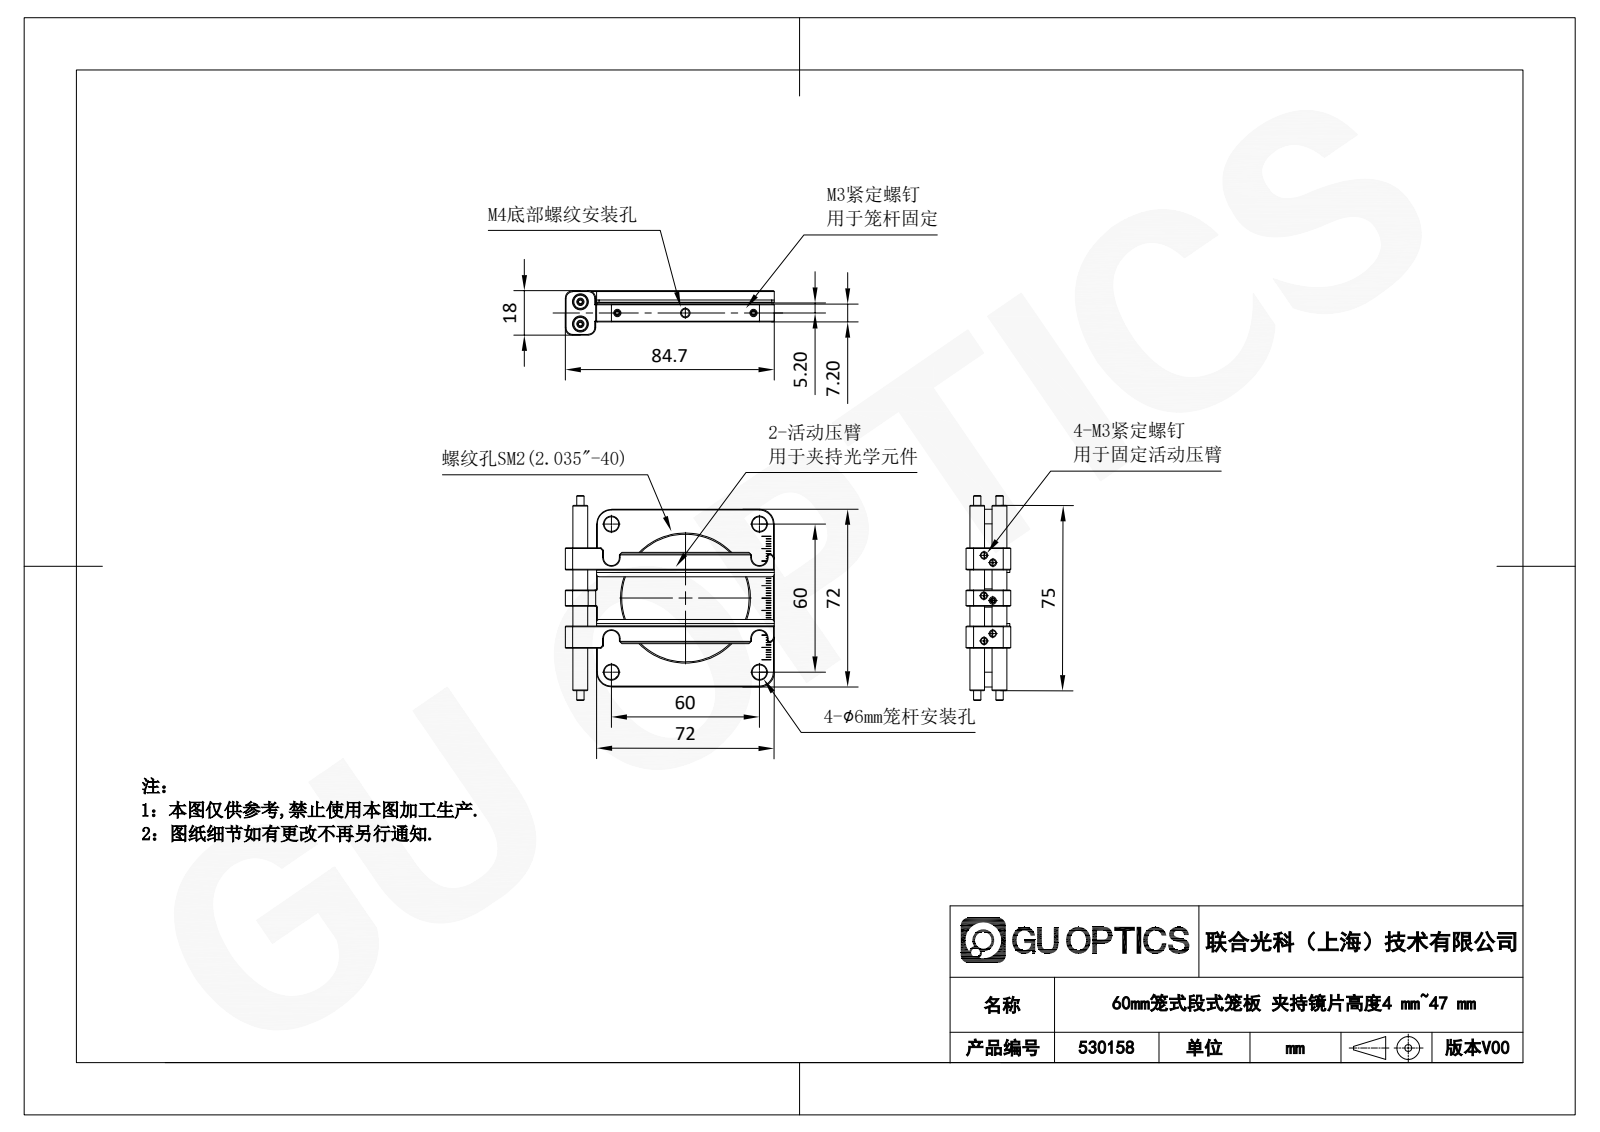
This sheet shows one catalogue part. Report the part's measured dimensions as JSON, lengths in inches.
{"part_name": "530158", "step_written_by": "SolidWorks 2020 (CONFIG_CONTROL_DESIGN)", "units": "inches", "bodies": {"solids": 16, "faces": 970, "planar": 745, "cylindrical": 65, "other": 160}, "overall_size": [3.335, 3.268, 0.709], "volume_in3": 2.099, "surface_area_in2": 34.2, "round_holes": [[0.098, 10], [0.236, 6], [0.13, 1], [2.035, 1]], "round_bosses_or_shafts": [[0.118, 5]], "partial_cylinders_radius": [[0.039, 5], [0.118, 4], [0.128, 4], [0.236, 4], [0.016, 2], [0.079, 2]], "face_to_face_distances": [0.283, 0.016, 0.299, 0.213, 0.496, 0.197, 0.97, 1.864, 2.835, 0.894], "hole_center_spacings": [1.67, 2.362, 0.185, 0.615, 1.087, 1.256, 1.685, 2.767]}
